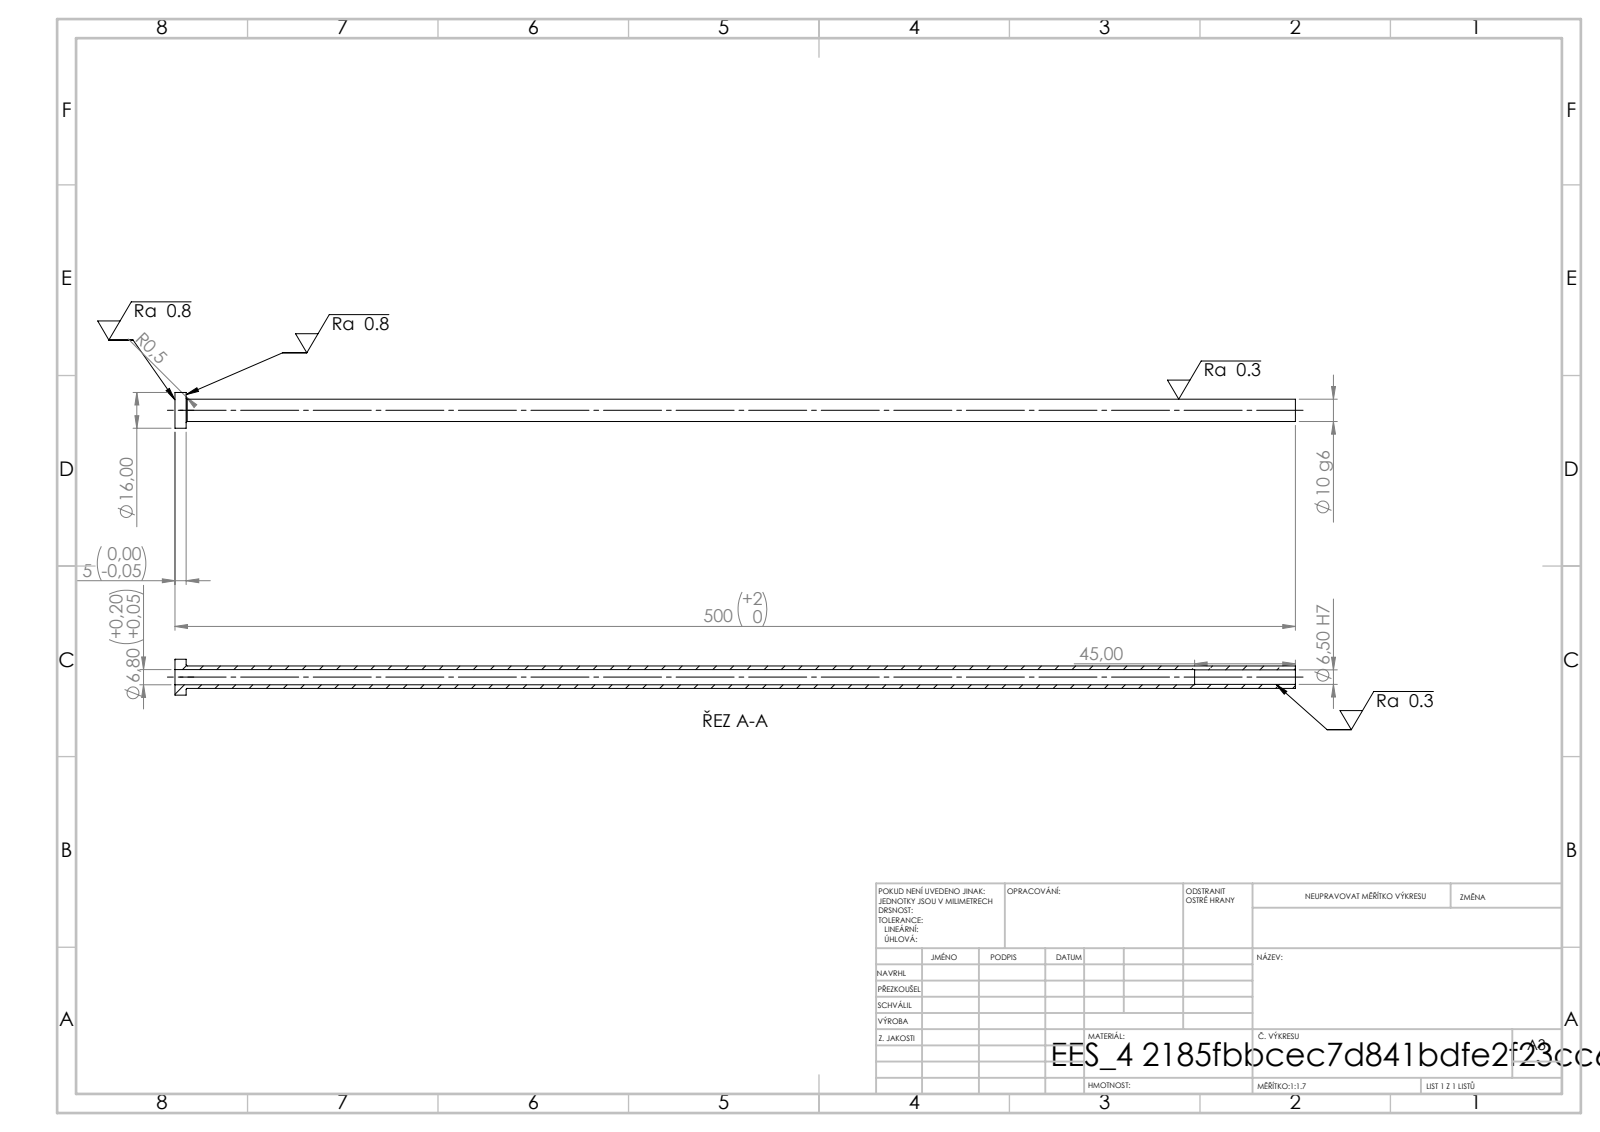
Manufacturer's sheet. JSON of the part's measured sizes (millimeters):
{"step_written_by": "SolidWorks 2019 (CONFIG_CONTROL_DESIGN)", "units": "millimeters", "bodies": {"solids": 1, "faces": 14, "planar": 4, "cylindrical": 8, "other": 2}, "overall_size": [500, 16, 16], "volume_mm3": 21867, "surface_area_mm2": 26770, "round_holes": [[6.5, 1], [6.8, 1]], "round_bosses_or_shafts": [[16, 1], [10, 1]], "face_to_face_distances": [5, 500, 495, 455, 450, 45]}
